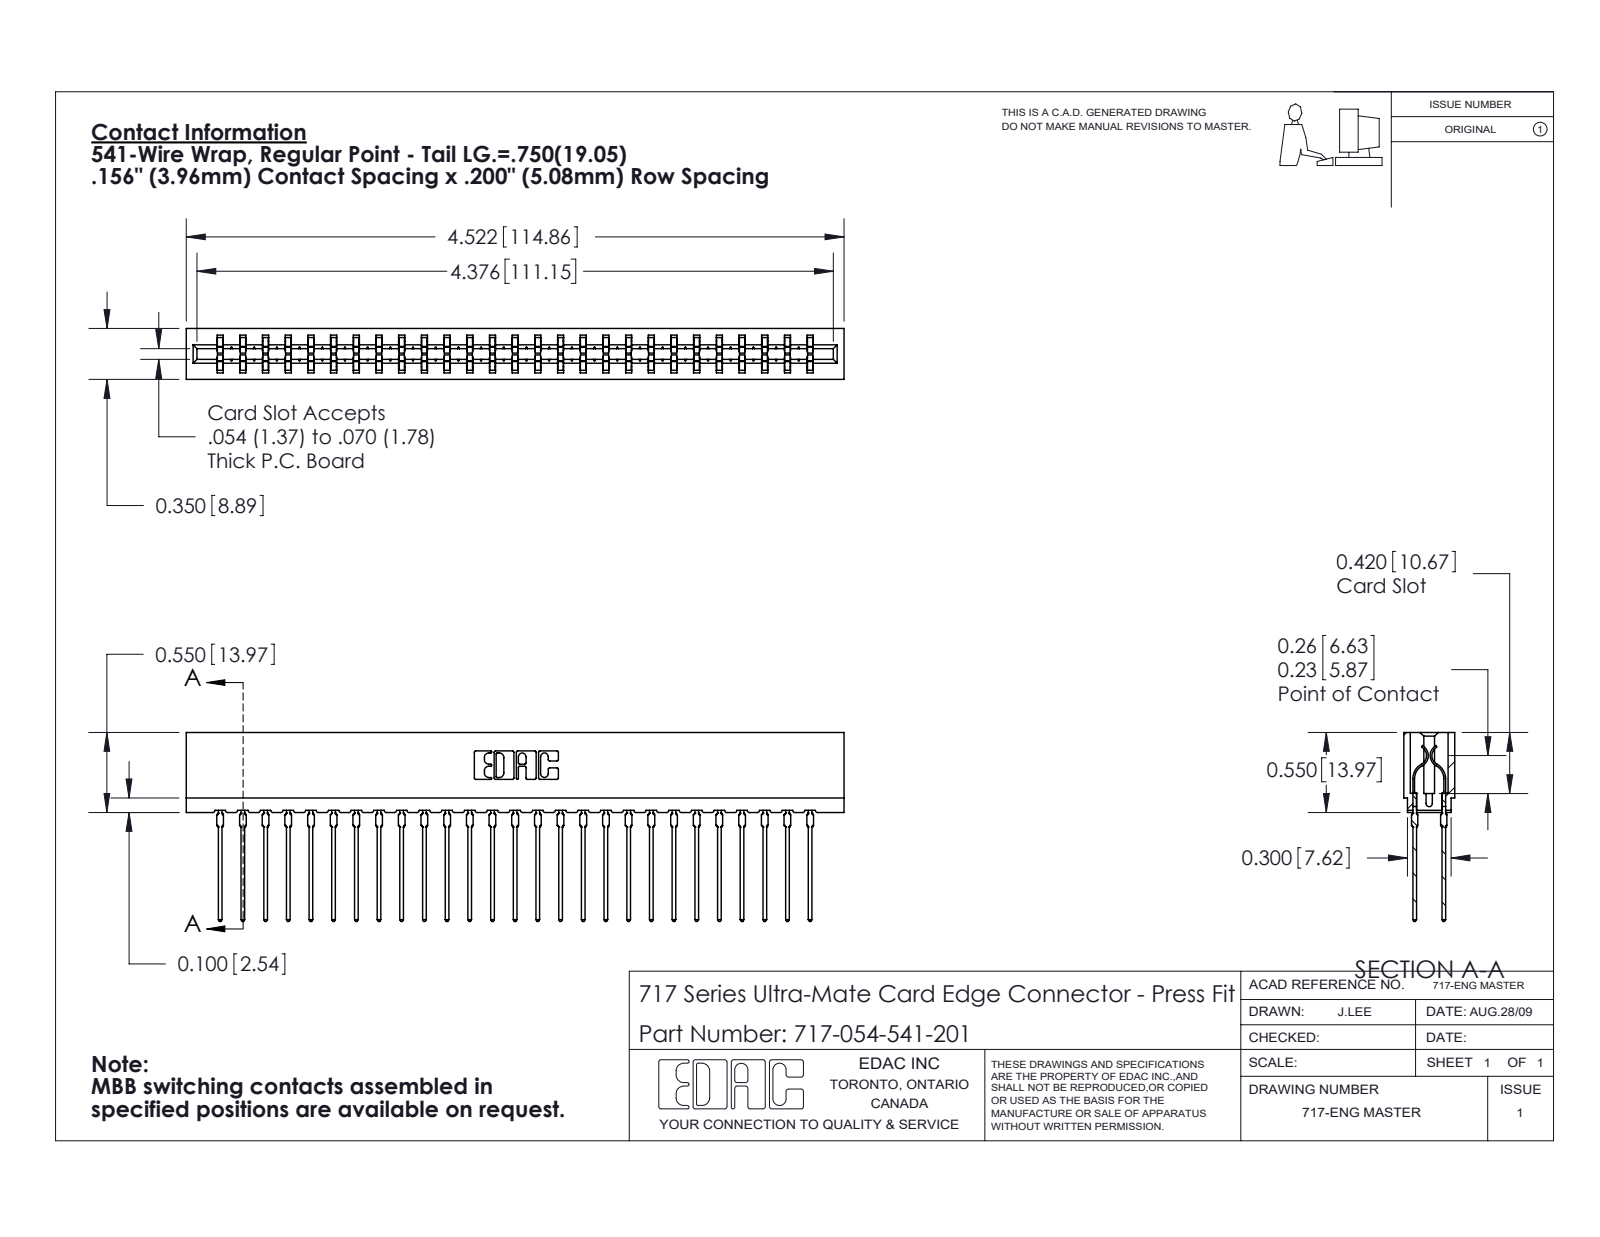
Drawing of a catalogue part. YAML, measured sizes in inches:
part_name: "745-292-001_541; 717 Part_Insulator Option - 06; 717-054-541-201"
step_written_by: "SolidWorks 2020 (CONFIG_CONTROL_DESIGN)"
units: inches
bodies: {solids: 55, faces: 4954, planar: 2565, cylindrical: 985, other: 1404}
overall_size: [4.522, 1.299, 0.35]
volume: 0.627
surface_area: 25.92
partial_cylinders:
  - {radius: 0.021, count: 108}
  - {radius: 0.015, count: 54}
  - {radius: 0.01, count: 22}
  - {radius: 0.005, count: 8}
  - {radius: 0.011, count: 8}
  - {radius: 0.007, count: 6}
  - {radius: 0.031, count: 6}
  - {radius: 0.026, count: 3}
face_to_face_distances: [0.212, 0.138, 0.35, 0.063, 0.287, 0.076, 0.149, 0.087, 0.263, 0.025]
